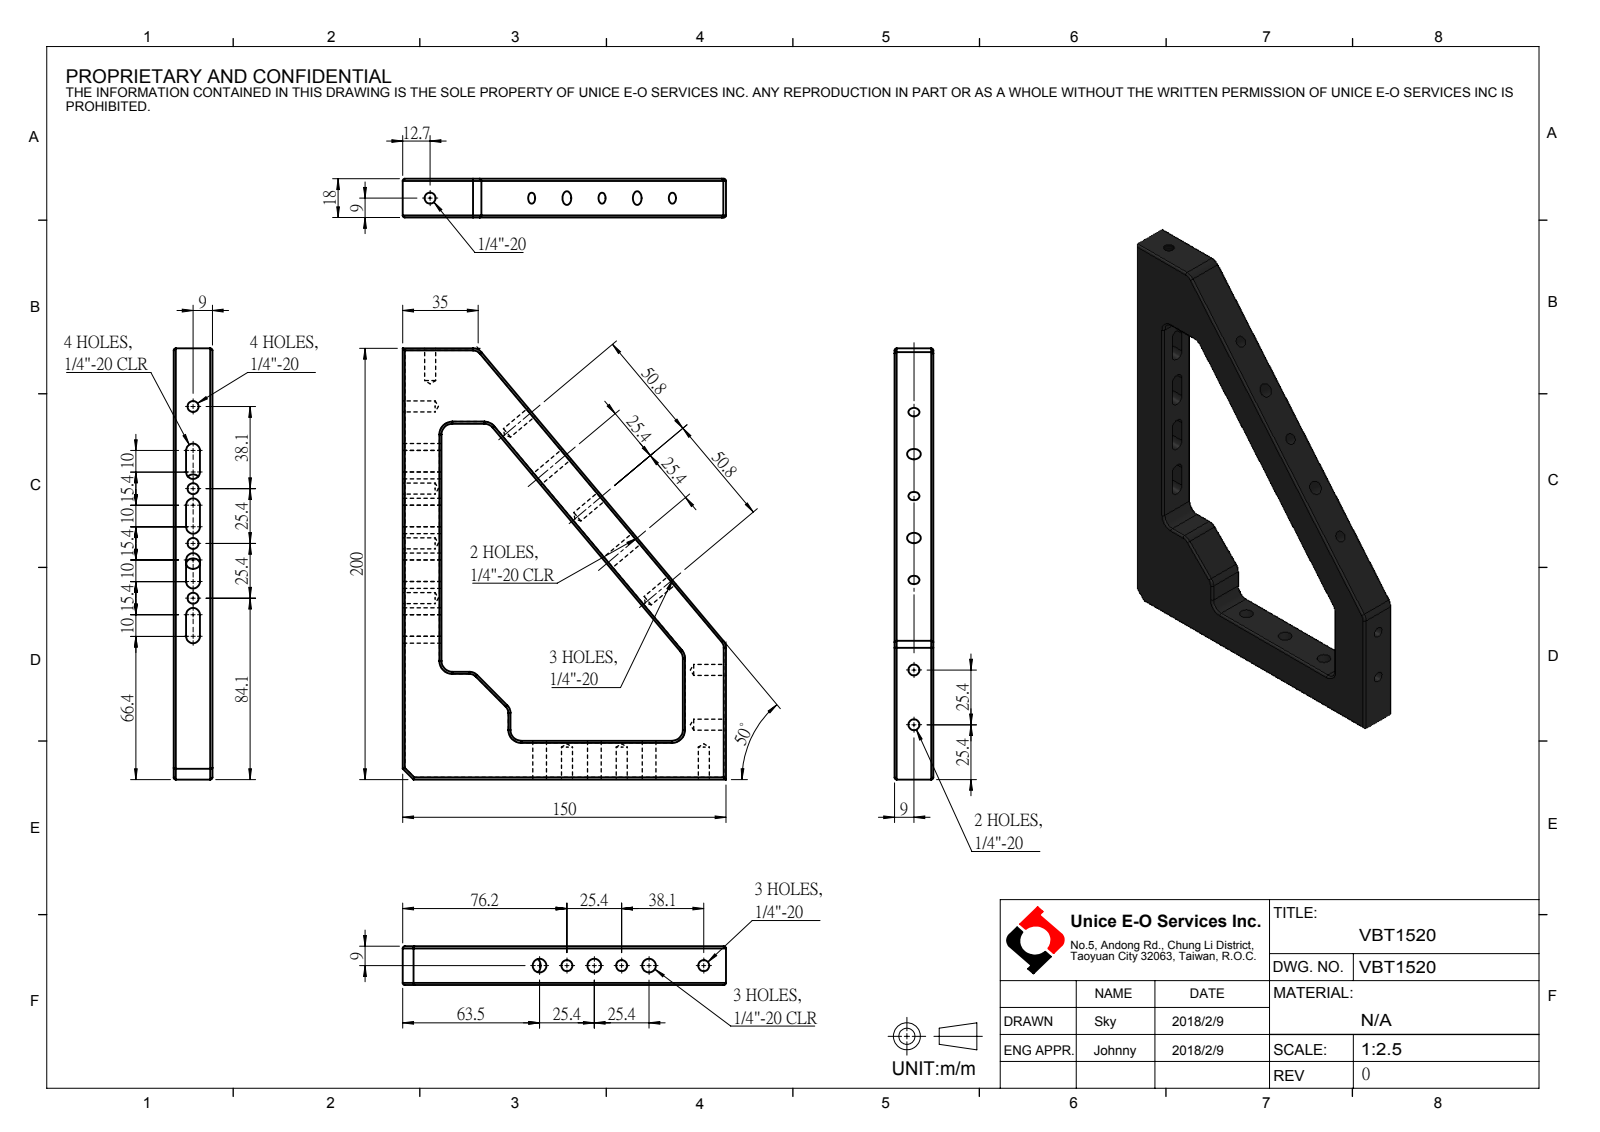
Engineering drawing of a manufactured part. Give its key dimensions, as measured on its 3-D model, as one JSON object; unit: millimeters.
{"part_name": "U-F1-VBT1520E1-D0; VBT1520", "step_written_by": "SolidWorks 2016 (AUTOMOTIVE_DESIGN)", "units": "millimeters", "bodies": {"solids": 1, "faces": 152, "planar": 24, "cylindrical": 82, "other": 46}, "overall_size": [200, 150, 18], "volume_mm3": 189843, "surface_area_mm2": 47737, "round_holes": [[5.11, 13], [6.35, 5]], "partial_cylinders_radius": [[1, 28], [5, 10], [3.2, 8]], "face_to_face_distances": [18, 18.54, 5.8, 12.2, 150, 132, 6.4, 20, 112, 130], "hole_center_spacings": [25.4, 50.8, 12.7, 38.1, 63.5, 76.2, 58.7, 84.1]}
